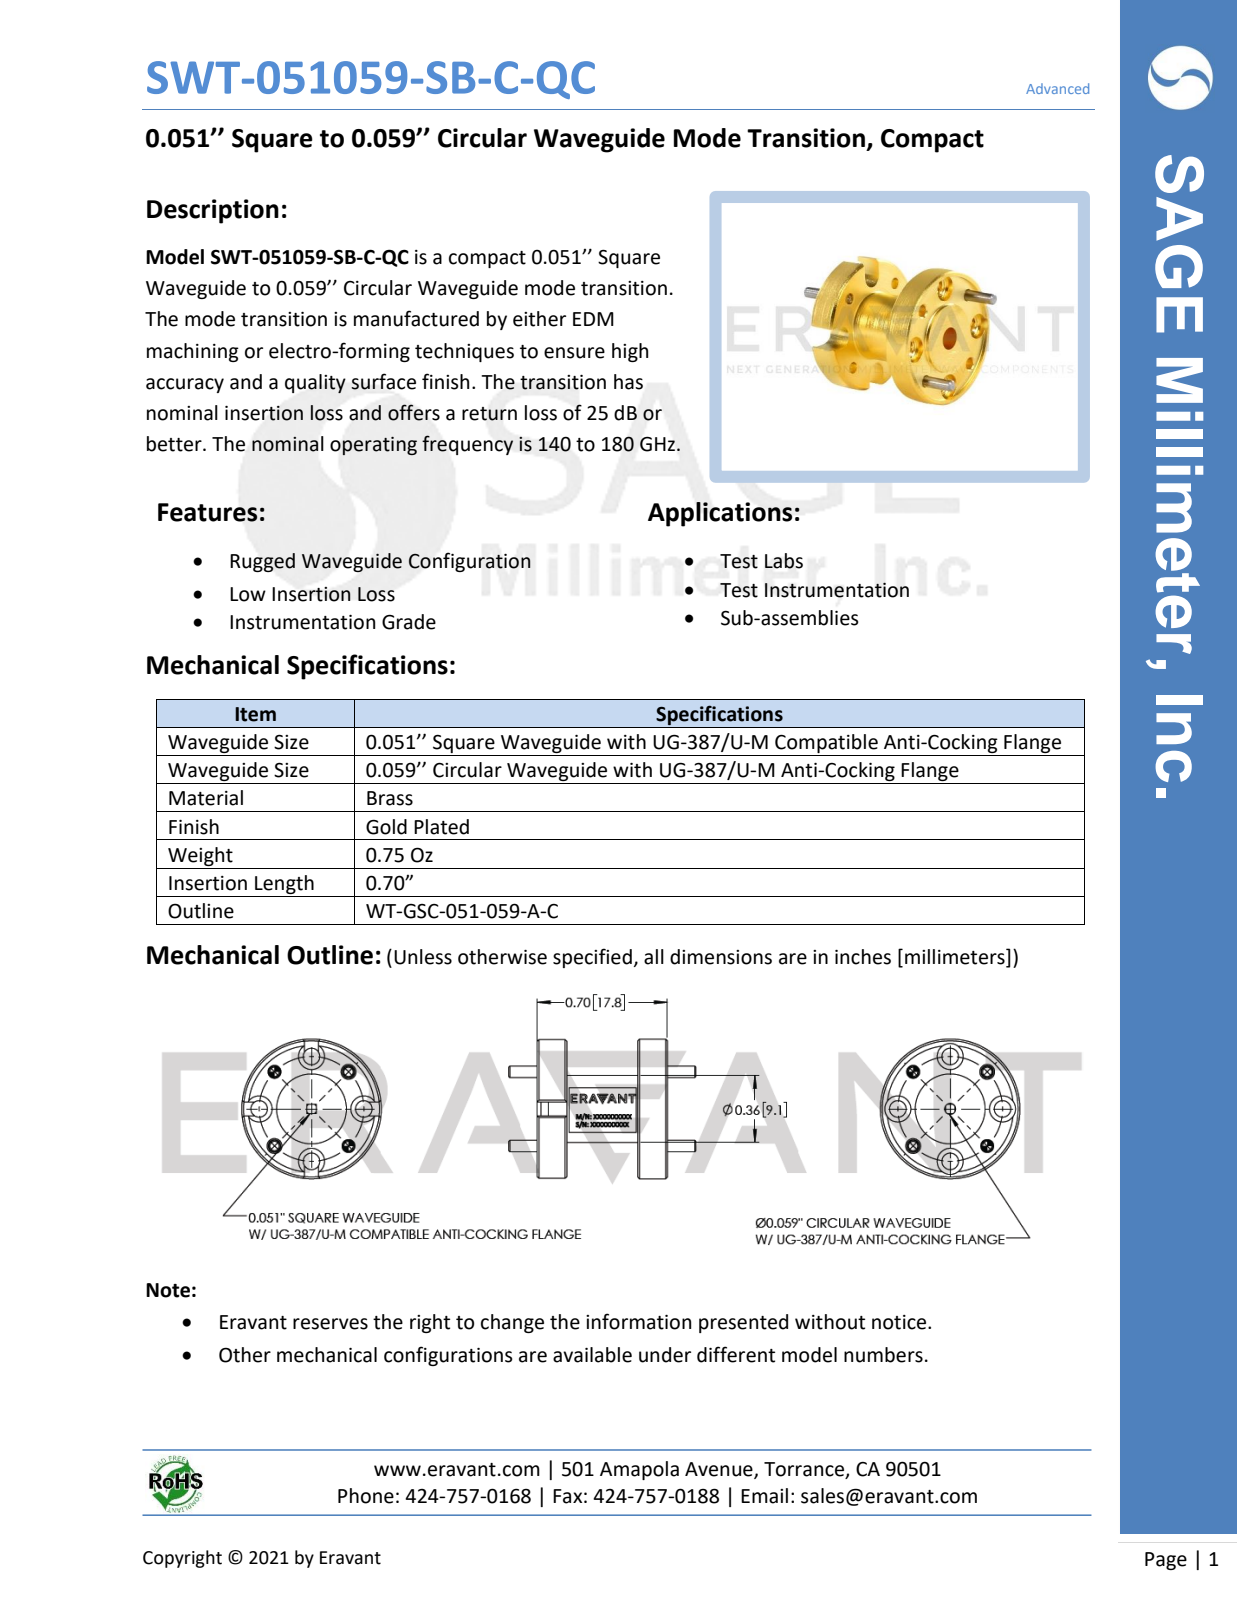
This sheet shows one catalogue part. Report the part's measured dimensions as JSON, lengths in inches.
{"part_name": "WT-GSC-051-059-A-C, Defeatured", "step_written_by": "SolidWorks 2021 (AUTOMOTIVE_DESIGN)", "units": "inches", "bodies": {"solids": 5, "faces": 175, "planar": 45, "cylindrical": 78, "other": 52}, "overall_size": [1.005, 0.75, 0.75], "volume_in3": 0.157, "surface_area_in2": 3.443, "round_holes": [[0.061, 4], [0.067, 4], [0.089, 4], [0.14, 4], [0.68, 1]], "round_bosses_or_shafts": [[0.063, 4], [0.75, 1], [0.375, 1], [0.36, 1]], "face_to_face_distances": [0.14, 0.52, 0.02, 0.16, 0.54, 0.68, 0.38, 0.66, 0.7, 0.06], "hole_center_spacings": [0.215, 0.281, 0.398, 0.519, 0.562]}
